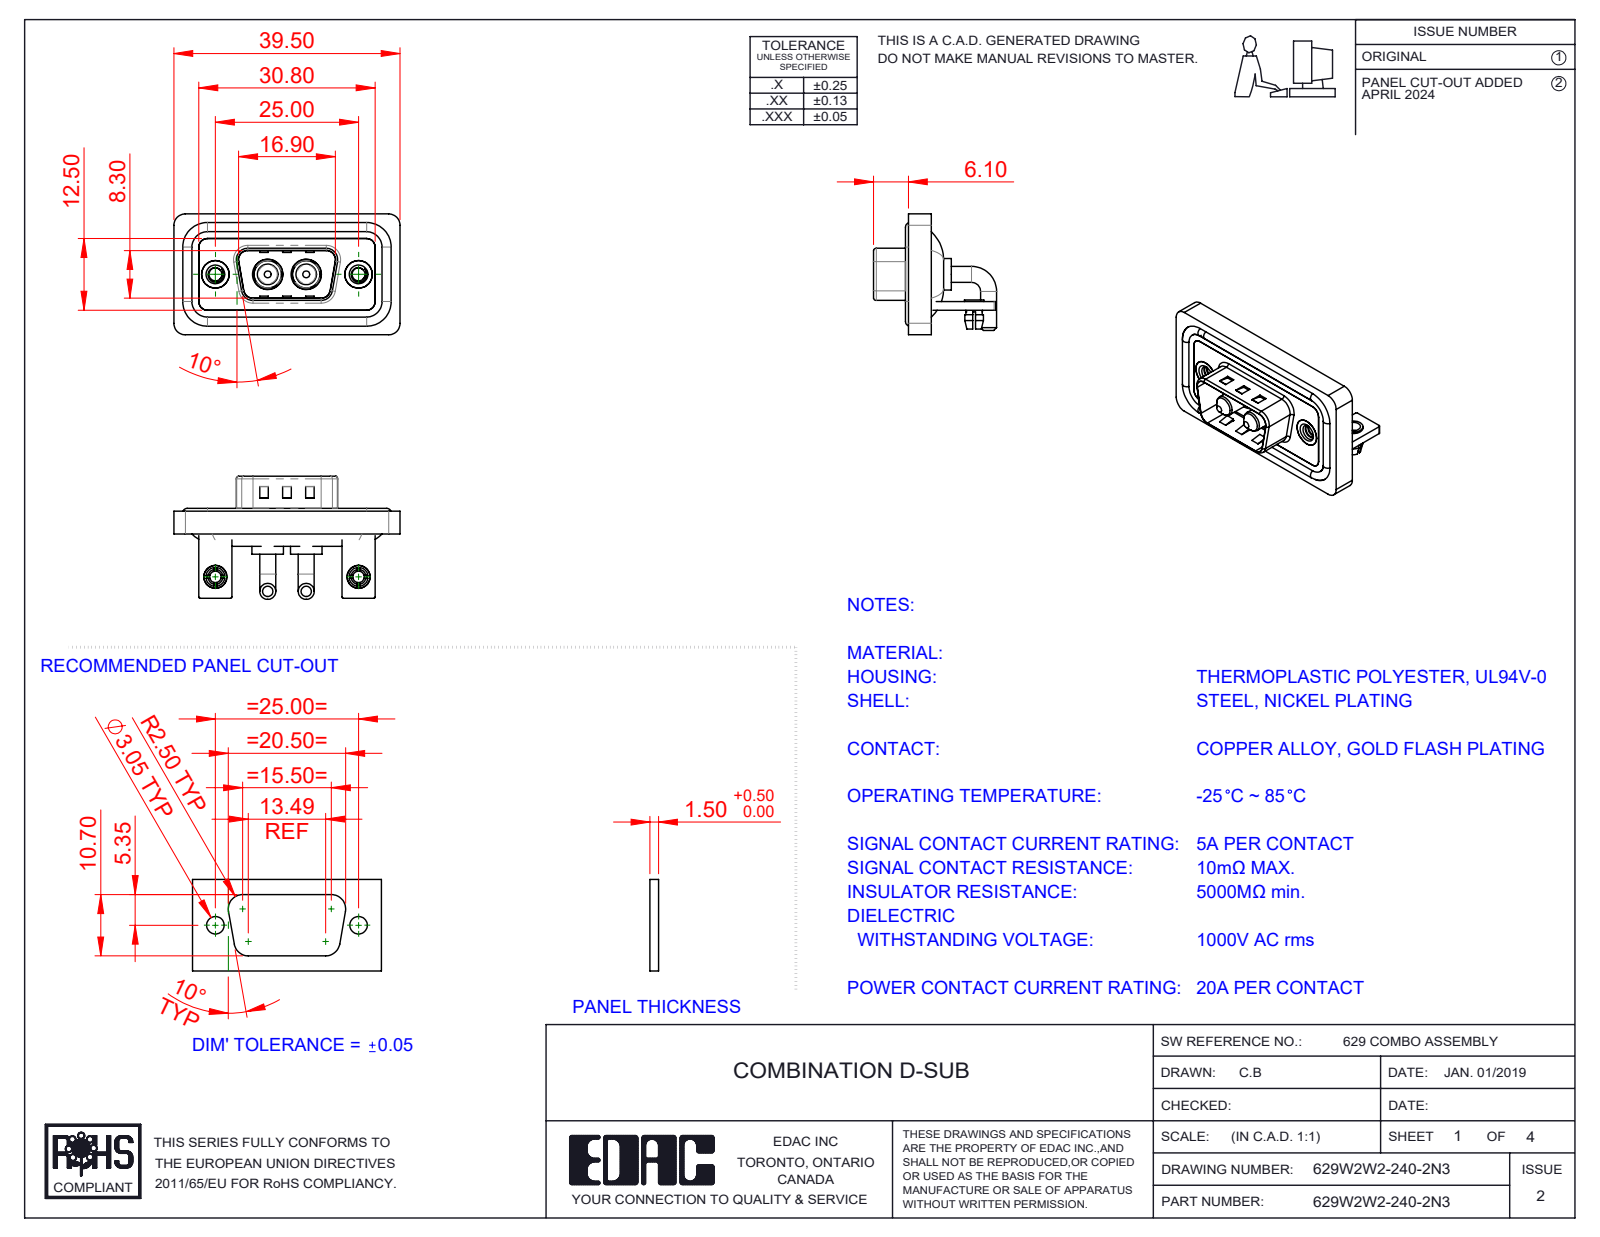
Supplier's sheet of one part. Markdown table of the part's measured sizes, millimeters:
| quantity | value |
| --- | --- |
| part name | 629Combo Stabilizer Bracket; 629Combo Shell Rear_09 Contacts; 629Combo Housing_2W2; 629Combo Board Lock (+5 more) |
| STEP written by | SolidWorks 2023 (CONFIG_CONTROL_DESIGN) |
| units | millimeters |
| bodies | 15 solids, 629 faces (233 planar, 272 cylindrical, 124 other) |
| overall size | 39.5 × 21.5 × 21.1 |
| volume | 4 898 mm³ |
| surface area | 7 964 mm² |
| round holes (diameter × count) | 2 × 2, 2.26 × 2, 2.5 × 2, 3.2 × 2, 4 × 2, 4.8 × 2, 4.85 × 2, 5 × 2, 5.3 × 2 |
| round bosses / shafts (diameter × count) | 2.8 × 4, 1.6 × 4, 5.5 × 2, 5.2 × 2, 4.9 × 2, 4.75 × 2, 4 × 2, 3.75 × 2 |
| partial cylindrical surfaces (radius × count) | 2 × 19, 1.5 × 18, 0.25 × 16, 0.5 × 9, 1.6 × 8, 0.6 × 4, 0.65 × 4, 0.9 × 4 |
| main face-to-face distances | 0.4, 1.5, 2.9, 0.8, 1.1, 1.2, 2.1, 1.6, 3.7, 2.5 |
| hole center spacings | 9.14, 15.86, 25, 6.72 |
